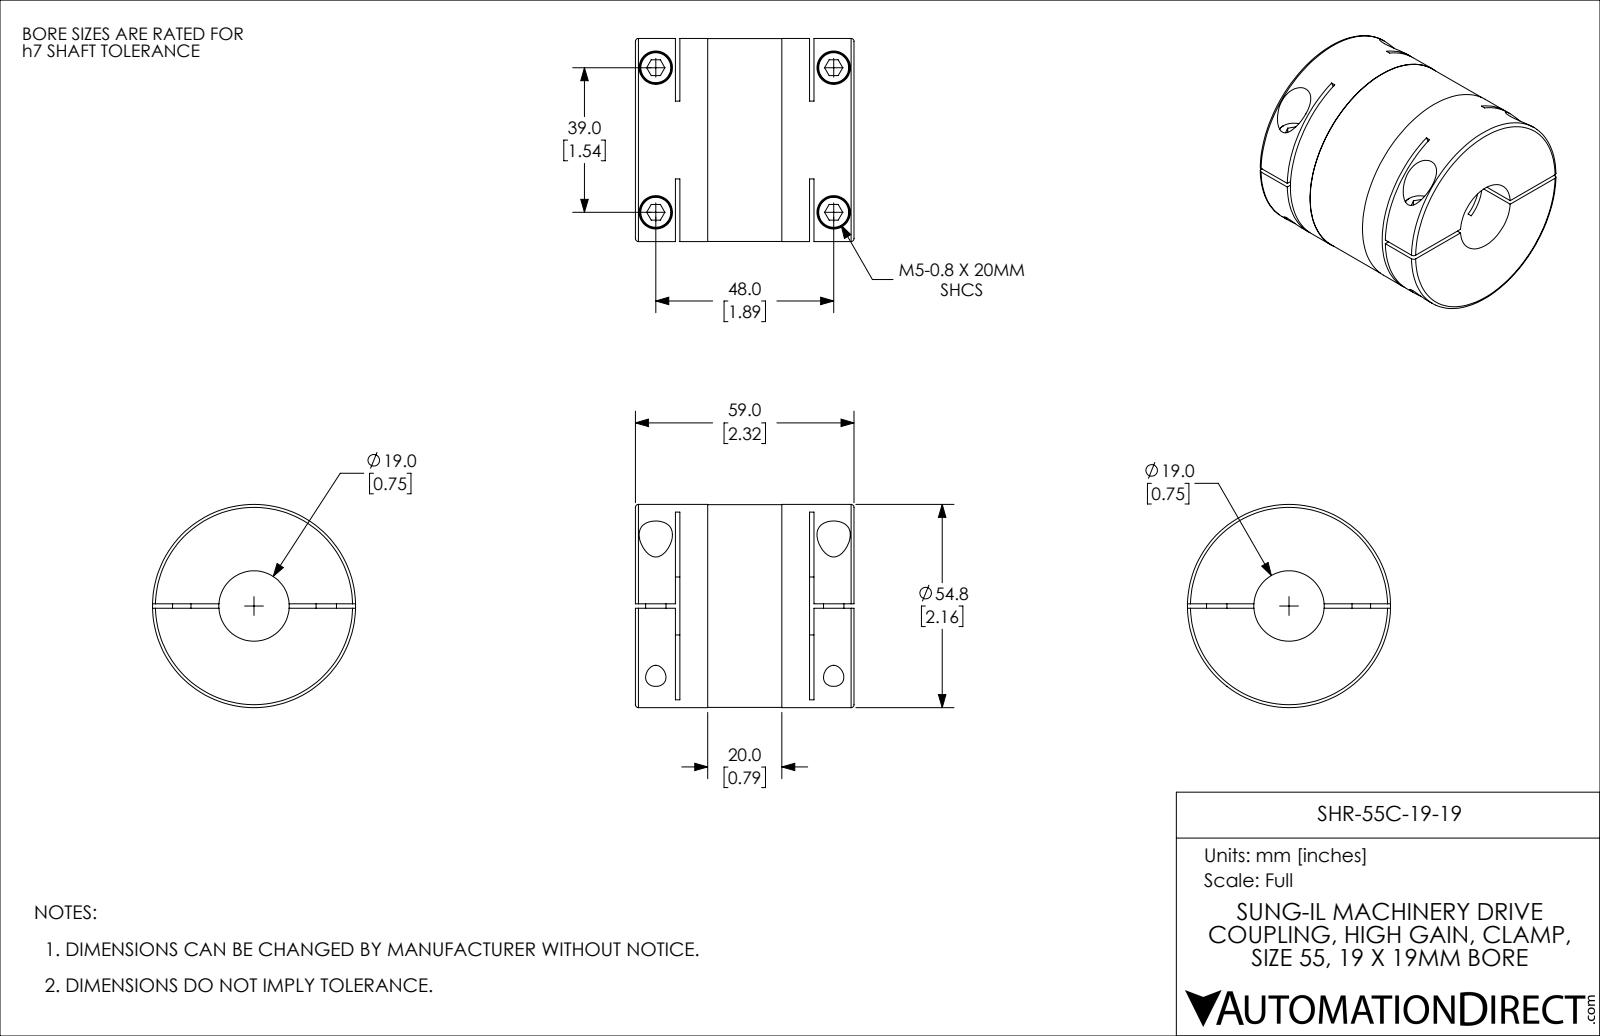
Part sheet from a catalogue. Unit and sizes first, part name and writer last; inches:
Units: inches
Overall size (bounding box): 2.323 × 2.157 × 2.157
Round holes (diameter × count): ⌀0.217 ×4, ⌀0.354 ×4, ⌀0.748 ×1, ⌀0.827 ×1
Round bosses / shafts (diameter × count): ⌀0.335 ×4, ⌀0.197 ×2, ⌀2.157 ×1, ⌀2.154 ×1
Partial cylindrical surfaces — rounded edges, fillets, slot ends (radius × count): R2.362 ×2
Main face-to-face distances: 0.047, 0.472, 1.85, 0.425, 1.898, 1.425, 2.323, 1.378, 1.472, 0.768
Hole centre spacings: 1.535, 1.89, 2.435
Volume: 6.937 in³ · Surface area: 44.13 in²
Bodies: 1 solid, 144 faces (70 planar, 58 cylindrical, 16 other)
Part name (STEP PRODUCT): SHR-55C-19-19
STEP written by: SolidWorks 2021 (CONFIG_CONTROL_DESIGN)
